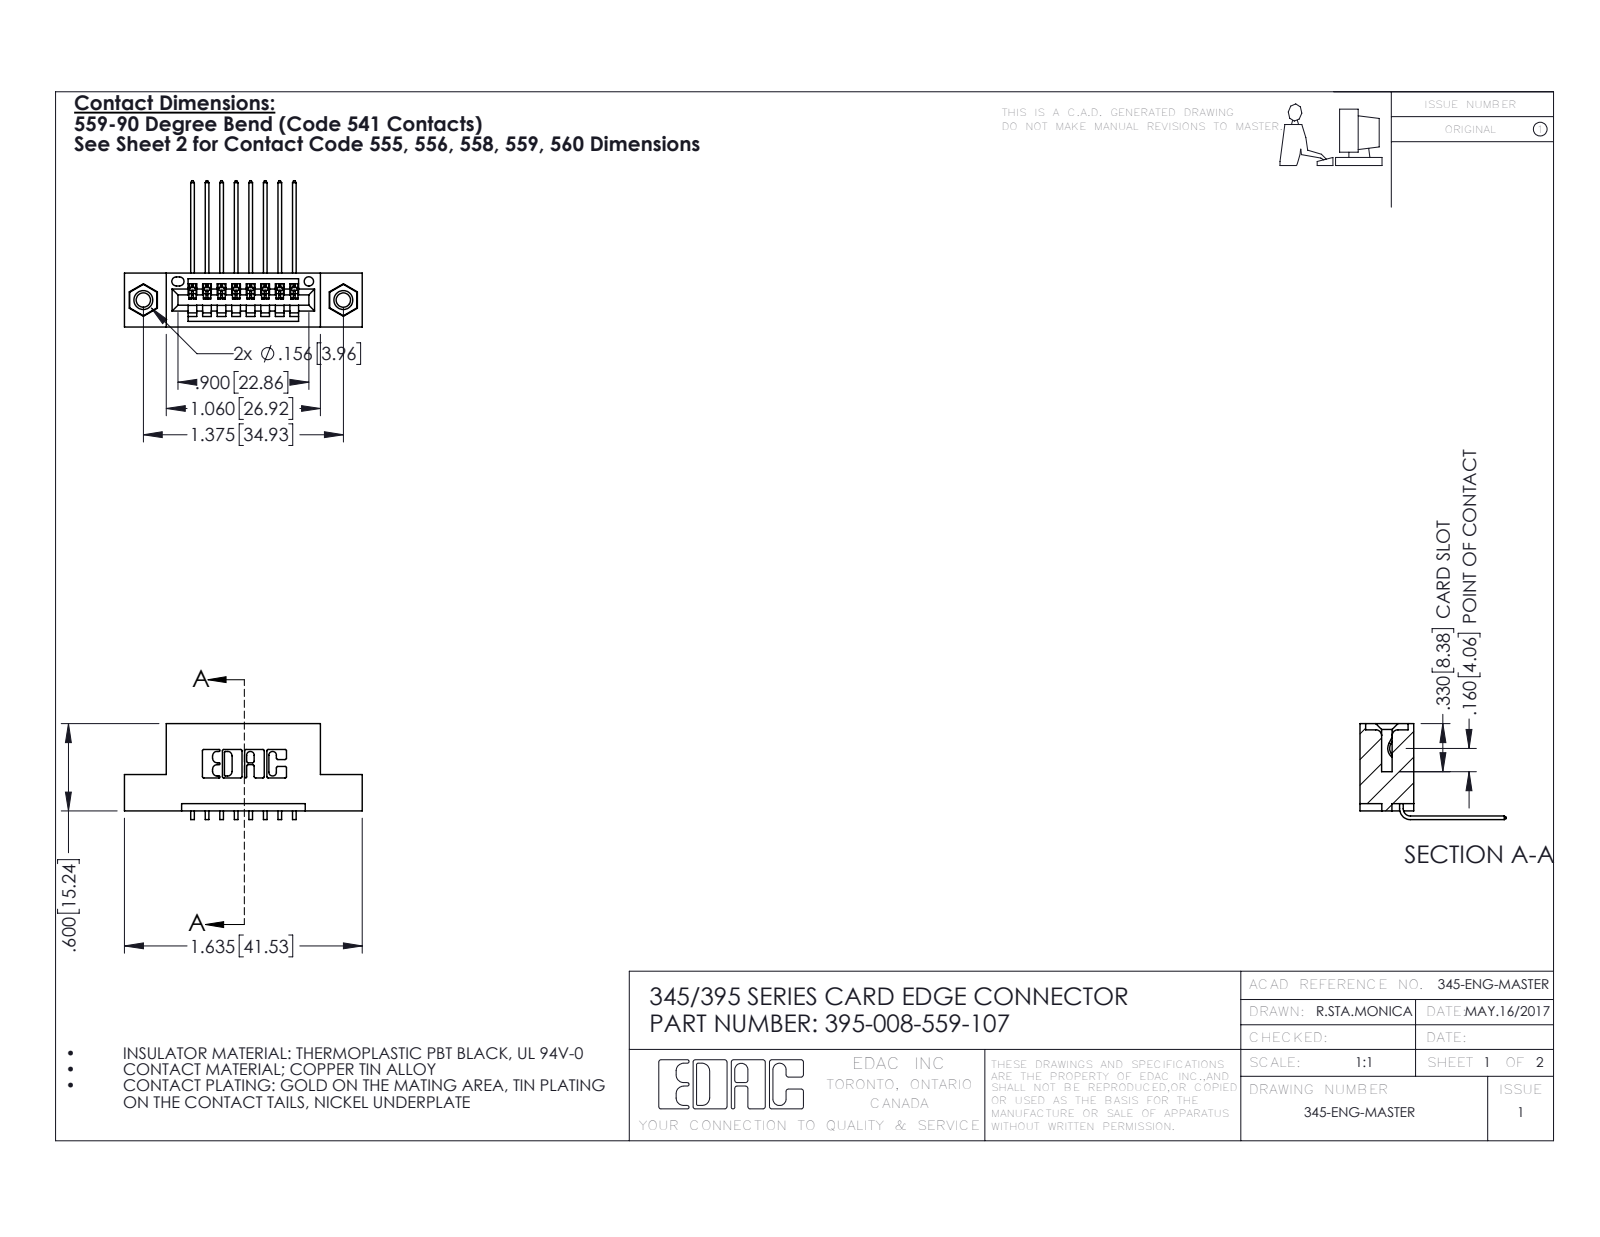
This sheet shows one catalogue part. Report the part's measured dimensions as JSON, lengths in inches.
{"part_name": "345-250-001_345-250-005-103; 345 Part_Flush Mounting Lugs - 0.156 Dia-TI; 395-008-559-107; 345-292-001_558 559 Tail - 1", "step_written_by": "SolidWorks 2016 (CONFIG_CONTROL_DESIGN)", "units": "inches", "bodies": {"solids": 11, "faces": 666, "planar": 448, "cylindrical": 202, "other": 16}, "overall_size": [1.635, 1.005, 0.659], "volume_in3": 0.225, "surface_area_in2": 7.155, "round_holes": [[0.098, 2], [0.125, 2], [0.156, 2], [0.064, 1]], "round_bosses_or_shafts": [[0.155, 2]], "partial_cylinders_radius": [[0.01, 22], [0.006, 16], [0.007, 6], [0.031, 6], [0.026, 3], [0.031, 2], [0.04, 2], [0.014, 1]], "face_to_face_distances": [0.2, 0.37, 0.1, 0.072, 0.298, 0.3, 0.06, 0.4, 0.098, 0.272], "hole_center_spacings": [0.27, 1.144, 1.375]}
